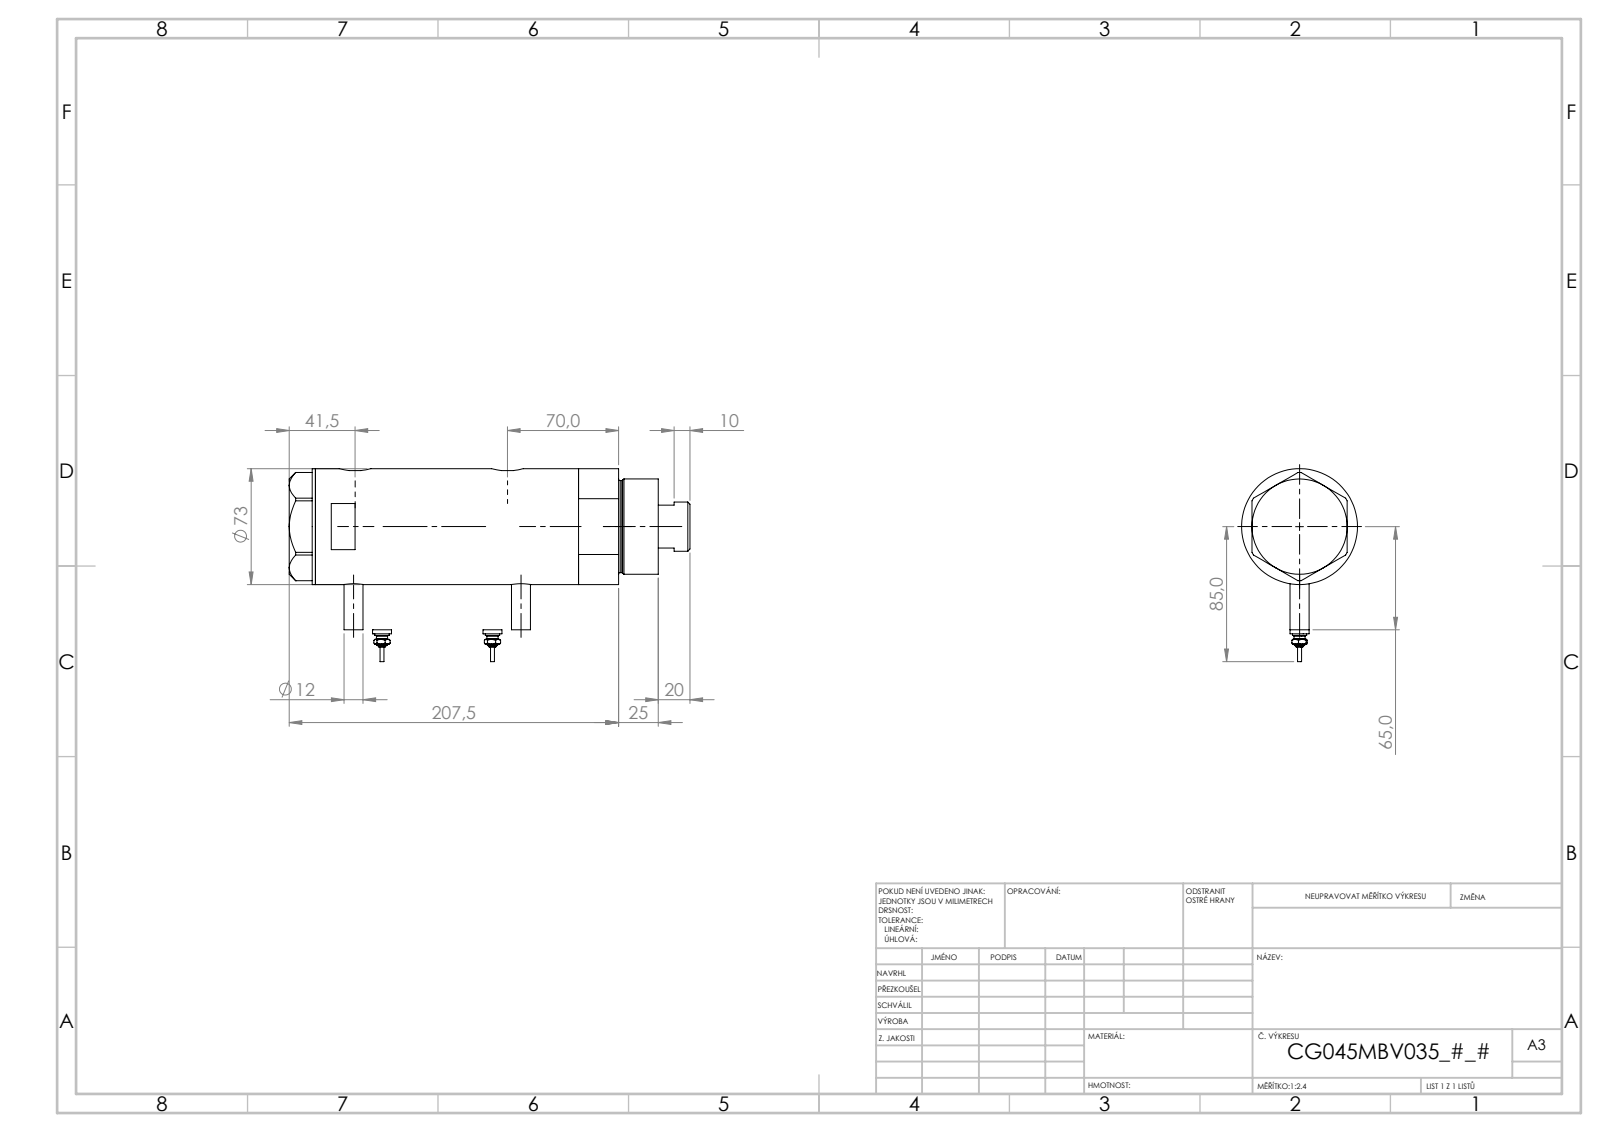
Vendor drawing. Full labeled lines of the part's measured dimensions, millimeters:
Part name (STEP PRODUCT): V270CG_VC; V270CG_SWITCH; V270CG_FRONT; V270CG_BACK (+1 more)
STEP written by: SolidWorks 2019 (CONFIG_CONTROL_DESIGN)
Units: millimetres
Bodies: 6 solids, 231 faces (78 planar, 79 cylindrical, 74 other)
Overall size (bounding box): 226.52 × 105.3 × 73
Volume: 788 584 mm³ · Surface area: 138 380 mm²
Round holes (diameter × count): ⌀5 ×2, ⌀12.5 ×2, ⌀13.16 ×2, ⌀10.5 ×1, ⌀32 ×1, ⌀33.5 ×1, ⌀45 ×1, ⌀48 ×1, ⌀64 ×1
Round bosses / shafts (diameter × count): ⌀12 ×2, ⌀9 ×2, ⌀7 ×2, ⌀5 ×2, ⌀4.34 ×2, ⌀2.4 ×2, ⌀73 ×1, ⌀60 ×1
Partial cylindrical surfaces — rounded edges, fillets, slot ends (radius × count): R10 ×2
Main face-to-face distances: 76.15, 16.5, 118.64, 102.14, 190.01, 87.87, 164.02, 42.5, 26, 76.14
Hole centre spacings: 86.65, 0.99, 1, 8.5, 8.51, 77.15, 78.14, 78.15
